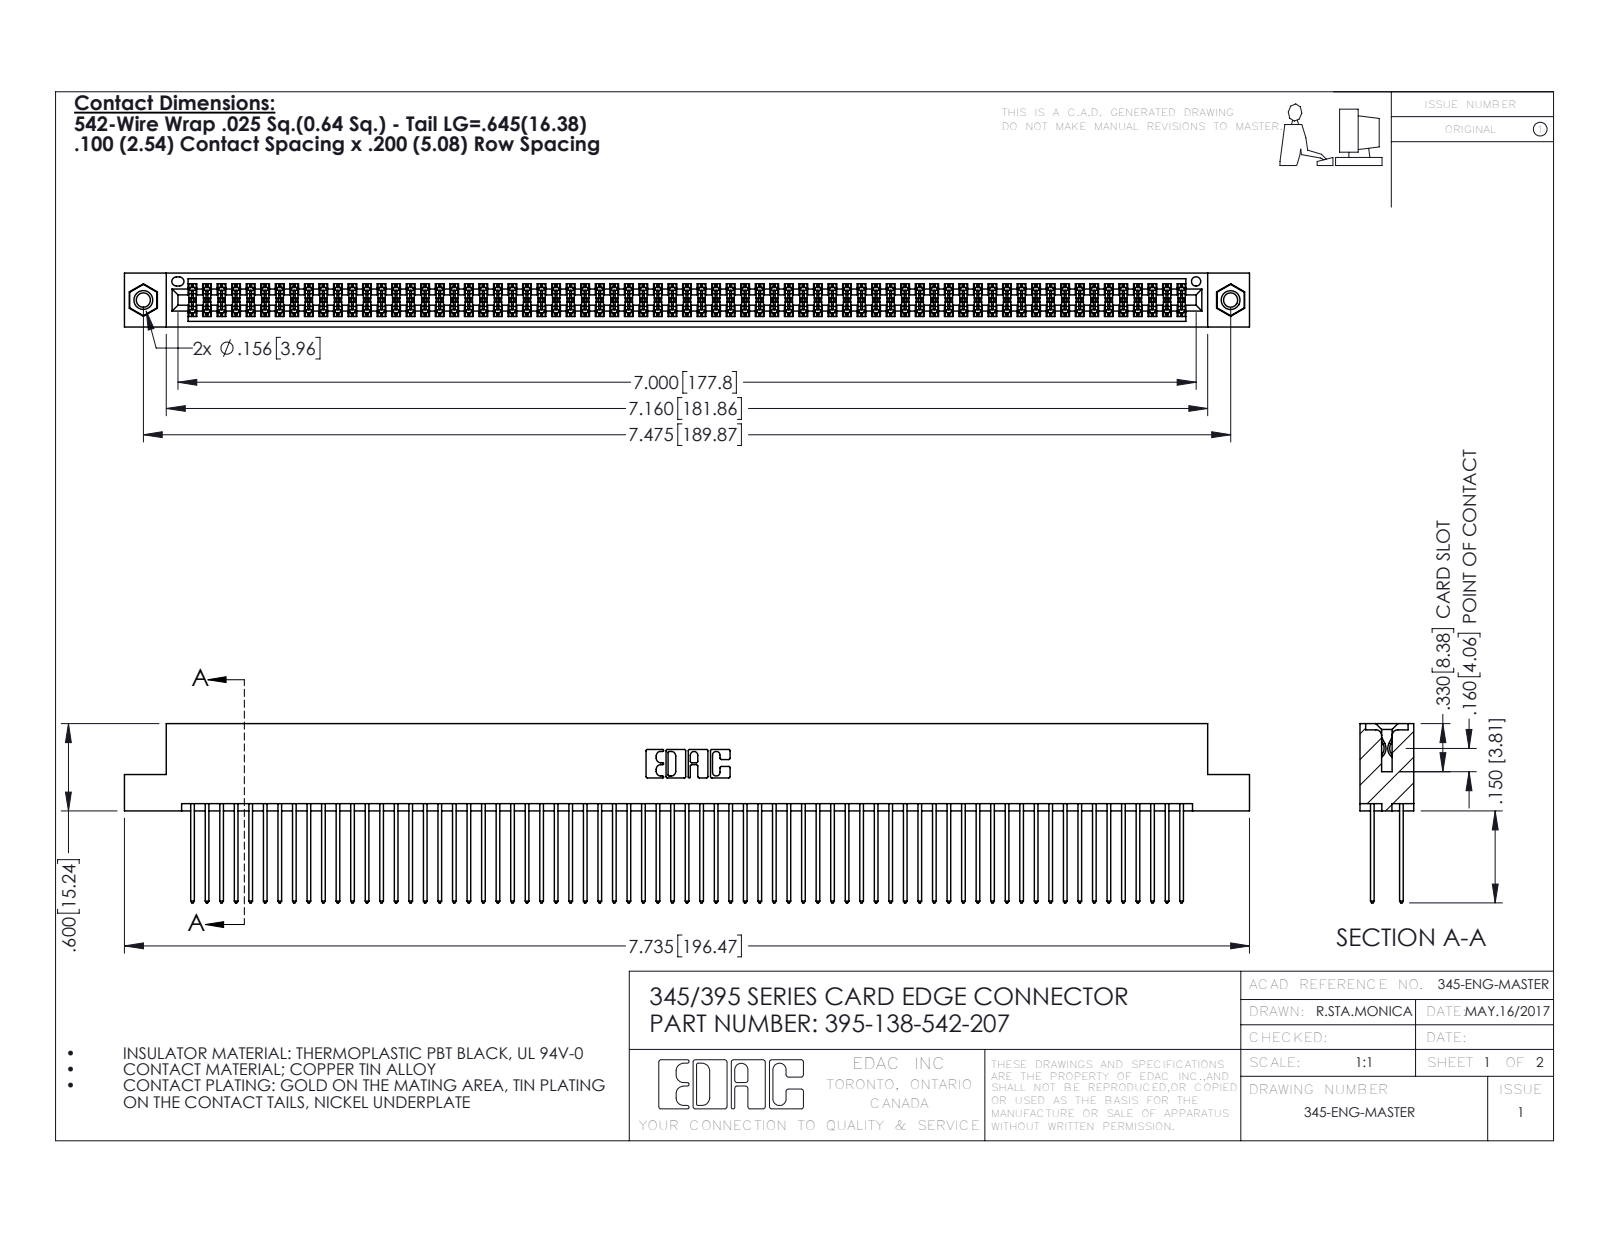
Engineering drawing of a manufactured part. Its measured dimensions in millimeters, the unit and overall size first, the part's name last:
Units: millimetres
Overall size (bounding box): 196.5 × 31.3 × 9.4
Round holes (diameter × count): ⌀2.5 ×2, ⌀3.2 ×2, ⌀4 ×2, ⌀1.6 ×1
Round bosses / shafts (diameter × count): ⌀3.9 ×2
Partial cylindrical surfaces — rounded edges, fillets, slot ends (radius × count): R0.2 ×207, R0.3 ×138, R0.3 ×22, R0.2 ×6, R0.8 ×6, R0.7 ×3, R0.4 ×2, R0.5 ×2
Main face-to-face distances: 1.8, 7.6, 5.1, 2.5, 6.9, 0.6, 5.7, 9.4, 4.4, 3.8
Hole centre spacings: 6.9, 183.9, 189.9
Volume: 19 960 mm³ · Surface area: 33 070 mm²
Bodies: 141 solids, 7086 faces (4666 planar, 2404 cylindrical, 16 other)
Part name (STEP PRODUCT): 345-292-001_345-293-142; 395-138-542-207; 345-250-001_345-250-005-103; 345 Part_Flush Mounting Lugs - 0.156 Dia-TI
STEP written by: SolidWorks 2016 (CONFIG_CONTROL_DESIGN)
